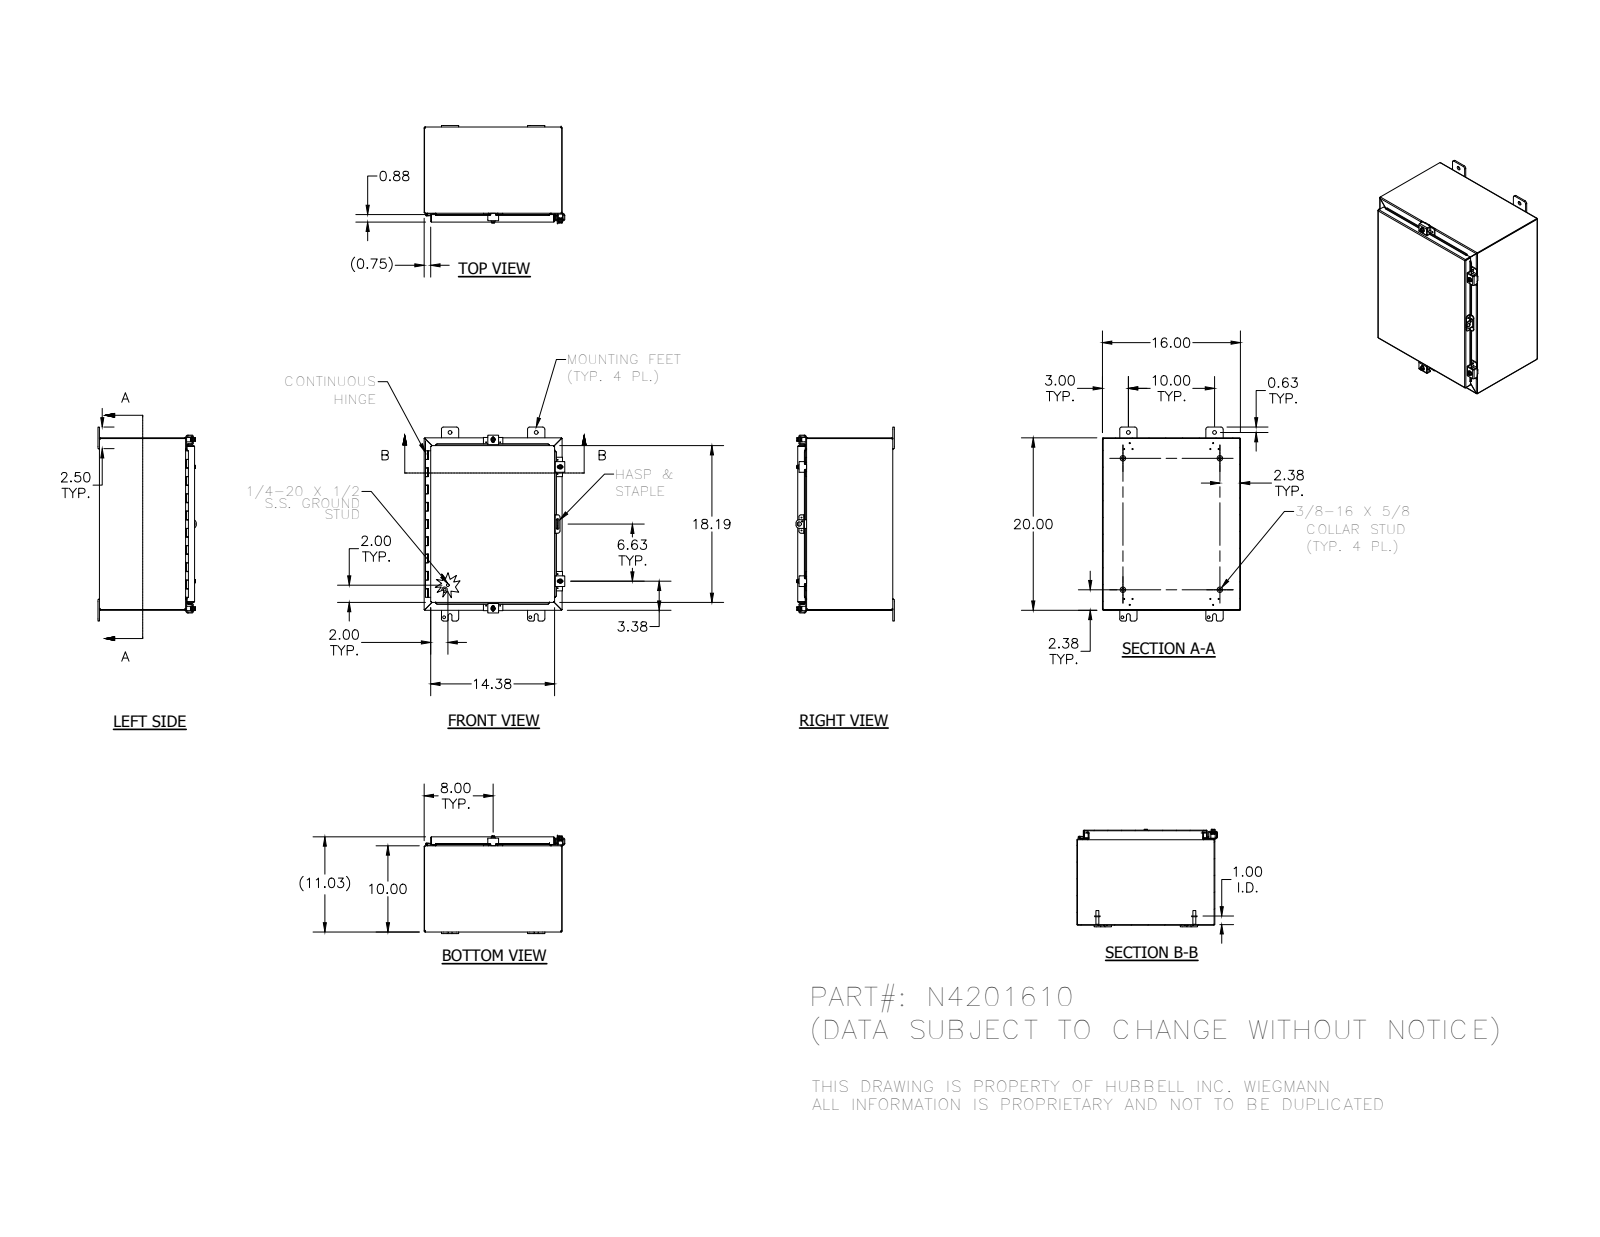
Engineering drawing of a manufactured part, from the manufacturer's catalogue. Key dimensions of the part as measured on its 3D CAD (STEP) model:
Part name (STEP PRODUCT): HFW30825-2_1; 328104L_1; 38420_1; 18x14_1 (+8 more)
STEP written by: SolidWorks 2014 (AUTOMOTIVE_DESIGN)
Units: inches
Bodies: 37 solids, 1614 faces (633 planar, 724 cylindrical, 257 other)
Overall size (bounding box): 22.5 × 16.311 × 11.41
Volume: 126.1 in³ · Surface area: 3 283 in²
Round holes (diameter × count): ⌀0.12 ×12, ⌀0.11 ×11, ⌀0.211 ×4, ⌀0.281 ×4, ⌀0.3 ×4, ⌀0.313 ×4, ⌀0.438 ×4, ⌀0.125 ×1, ⌀0.156 ×1, ⌀0.5 ×1
Round bosses / shafts (diameter × count): ⌀0.25 ×6, ⌀0.625 ×4, ⌀0.52 ×4, ⌀0.5 ×4, ⌀0.35 ×4, ⌀0.33 ×4, ⌀0.115 ×2, ⌀0.337 ×1
Partial cylindrical surfaces — rounded edges, fillets, slot ends (radius × count): R0.03 ×49, R0.062 ×33, R0.125 ×33, R0.25 ×29, R0.031 ×23, R0.105 ×23, R0.07 ×8, R0.141 ×8
Main face-to-face distances: 0.074, 10.959, 15.926, 19.926, 10.885, 11.033, 15.852, 16, 9.926, 1.033
Hole centre spacings: 10, 0.876, 19.294, 0.759, 0.839, 0.94, 0.969, 1.593
